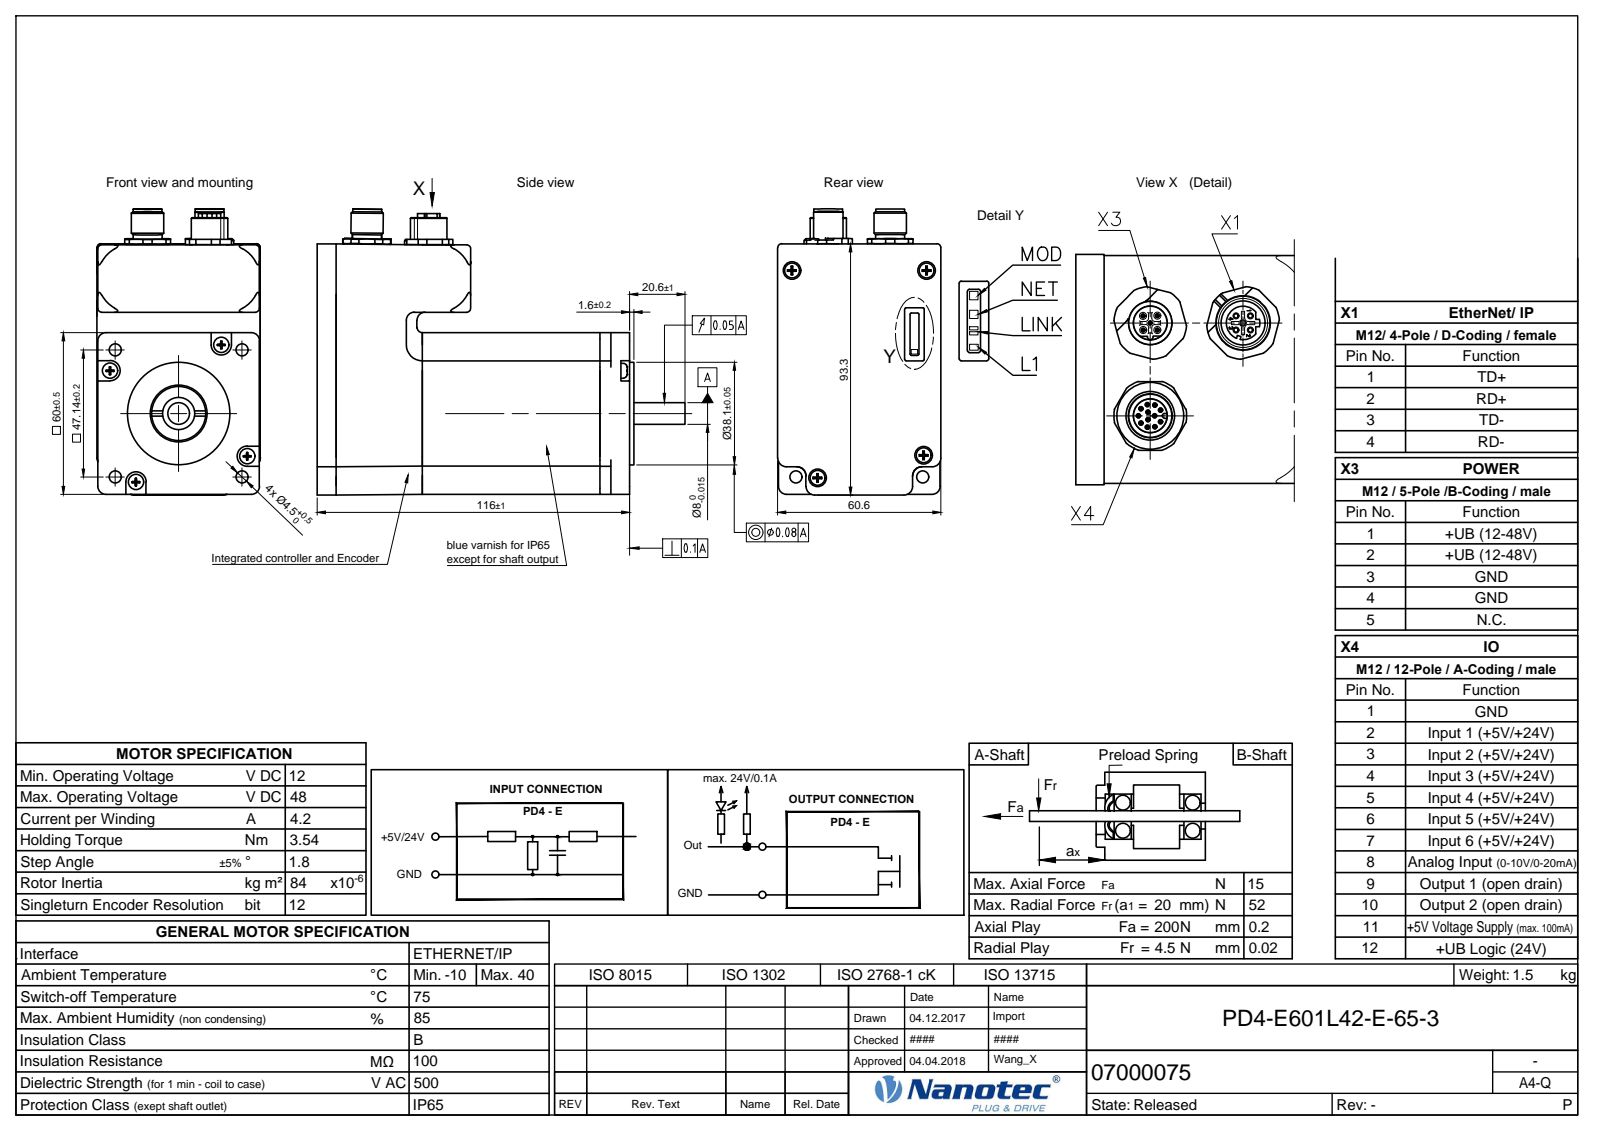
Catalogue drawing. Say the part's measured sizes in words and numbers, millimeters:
The part is named "PD4-E601L42-E-65-3". Its 3-D file was written by "Autodesk Inventor 2017 (AUTOMOTIVE_DESIGN)". It is 16 solids with 1293 faces: 573 planar, 426 cylindrical and 294 other. Overall it measures 136.6 by 106.27 by 60.6 millimeters. Its volume is 344 696 cubic millimeters and its surface area 92 517 square millimeters. Round holes: 12 of diameter 1.2, 8 of diameter 2.46, 5 of diameter 1.1, 5 of diameter 15.3, 4 of diameter 1.7, 4 of diameter 3.2, 4 of diameter 3.4, 4 of diameter 4.5, 2 of diameter 1.57, 2 of diameter 2.01, 2 of diameter 4.92, 2 of diameter 10.5. Round bosses or shafts: 12 of diameter 1.1, 12 of diameter 0.63, 9 of diameter 1.3, 8 of diameter 3, 5 of diameter 1, 4 of diameter 5.5, 4 of diameter 2.73, 4 of diameter 2.69. Partial cylindrical surfaces (rounded edges, fillets, slot ends): 45 of radius 2, 18 of radius 0.2, 16 of radius 0.3, 16 of radius 0.5, 16 of radius 1.5, 12 of radius 0.1, 12 of radius 3.5, 10 of radius 0.15. The main face-to-face distances are 60, 105, 39, 35.7, 66, 3.3, 101.7, 55.7, 4.3, 2. The hole center spacings are 2.9, 3.54, 2.5, 1.87, 4.83, 1.1, 1.34, 1.86.
